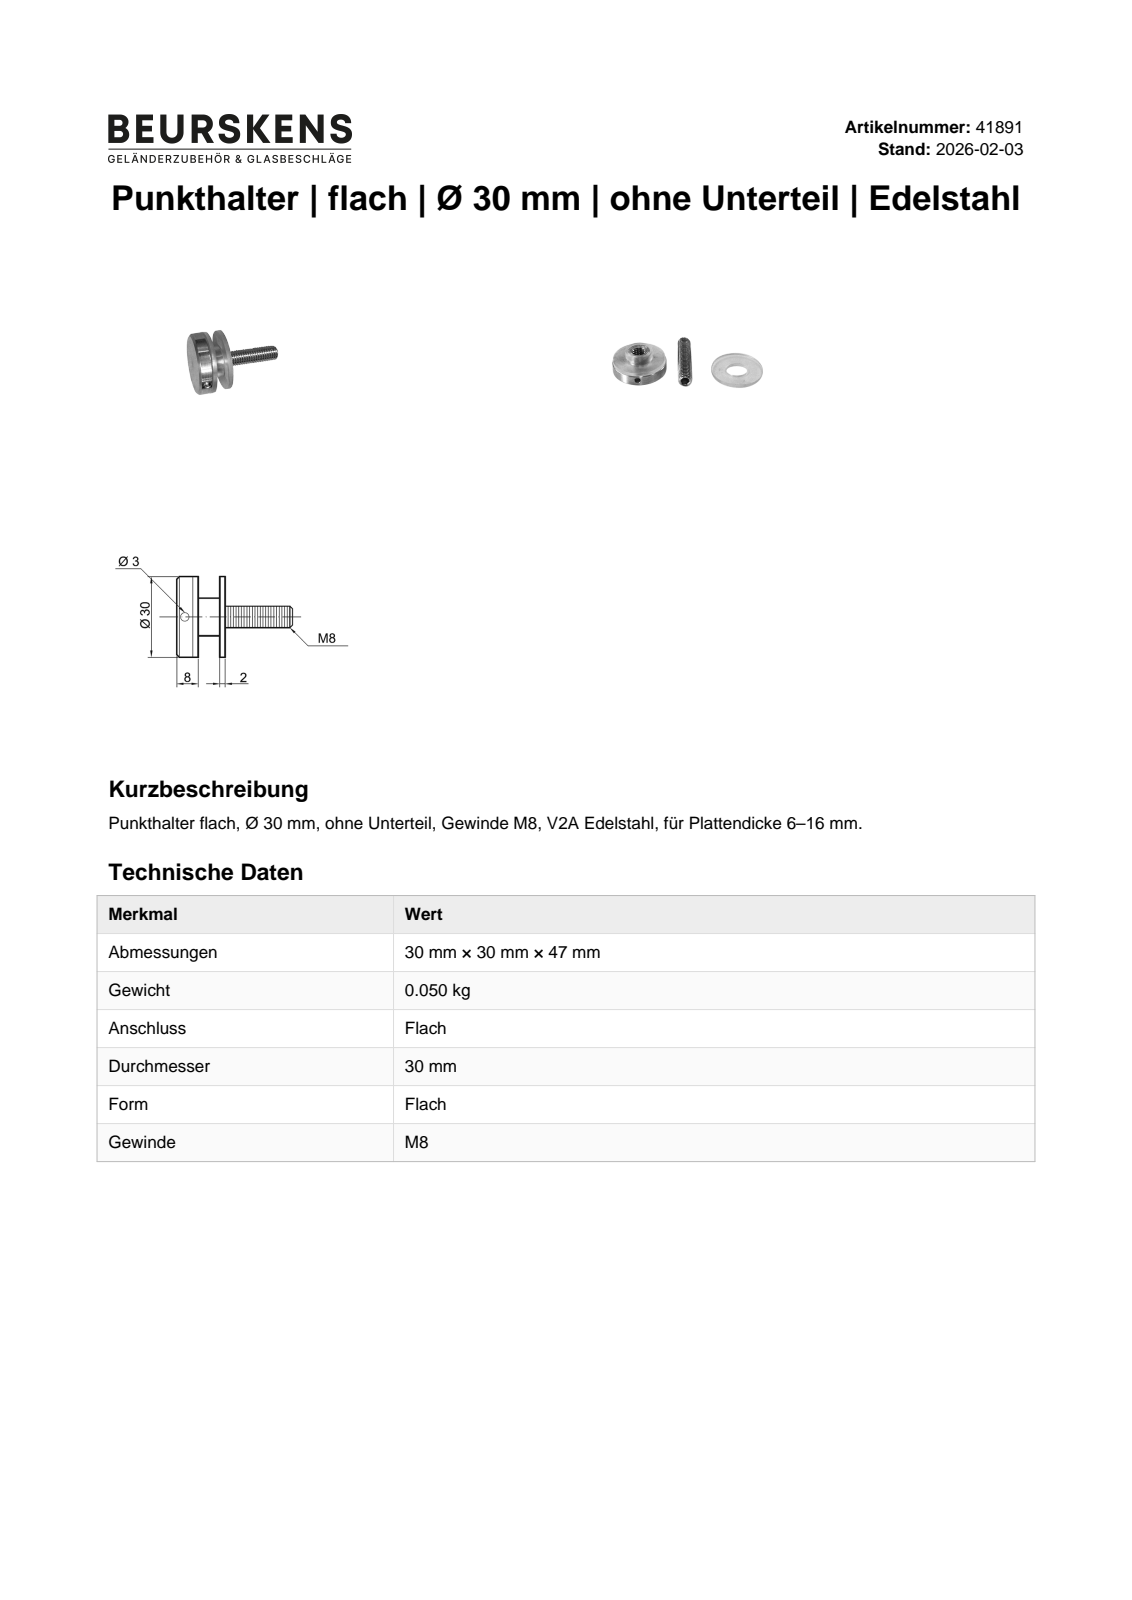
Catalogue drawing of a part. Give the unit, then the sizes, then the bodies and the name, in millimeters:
Units: millimetres
Overall size (bounding box): 42.5 × 30 × 30
Round holes (diameter × count): ⌀3 ×1, ⌀8 ×1, ⌀12 ×1
Round bosses / shafts (diameter × count): ⌀30 ×1, ⌀15 ×1
Main face-to-face distances: 7, 1.5, 6, 13, 8.5, 14.5, 5.5, 7.5, 5, 12
Volume: 8 499 mm³ · Surface area: 6 845 mm²
Bodies: 4 solids, 33 faces (18 planar, 10 cylindrical, 5 other)
Part name (STEP PRODUCT): 41891; Kopf 41891; DIN 913 - M8 x 40; Gummi 30er Punkthaler (+1 more)
STEP written by: Autodesk Inventor 2023 (AUTOMOTIVE_DESIGN)
